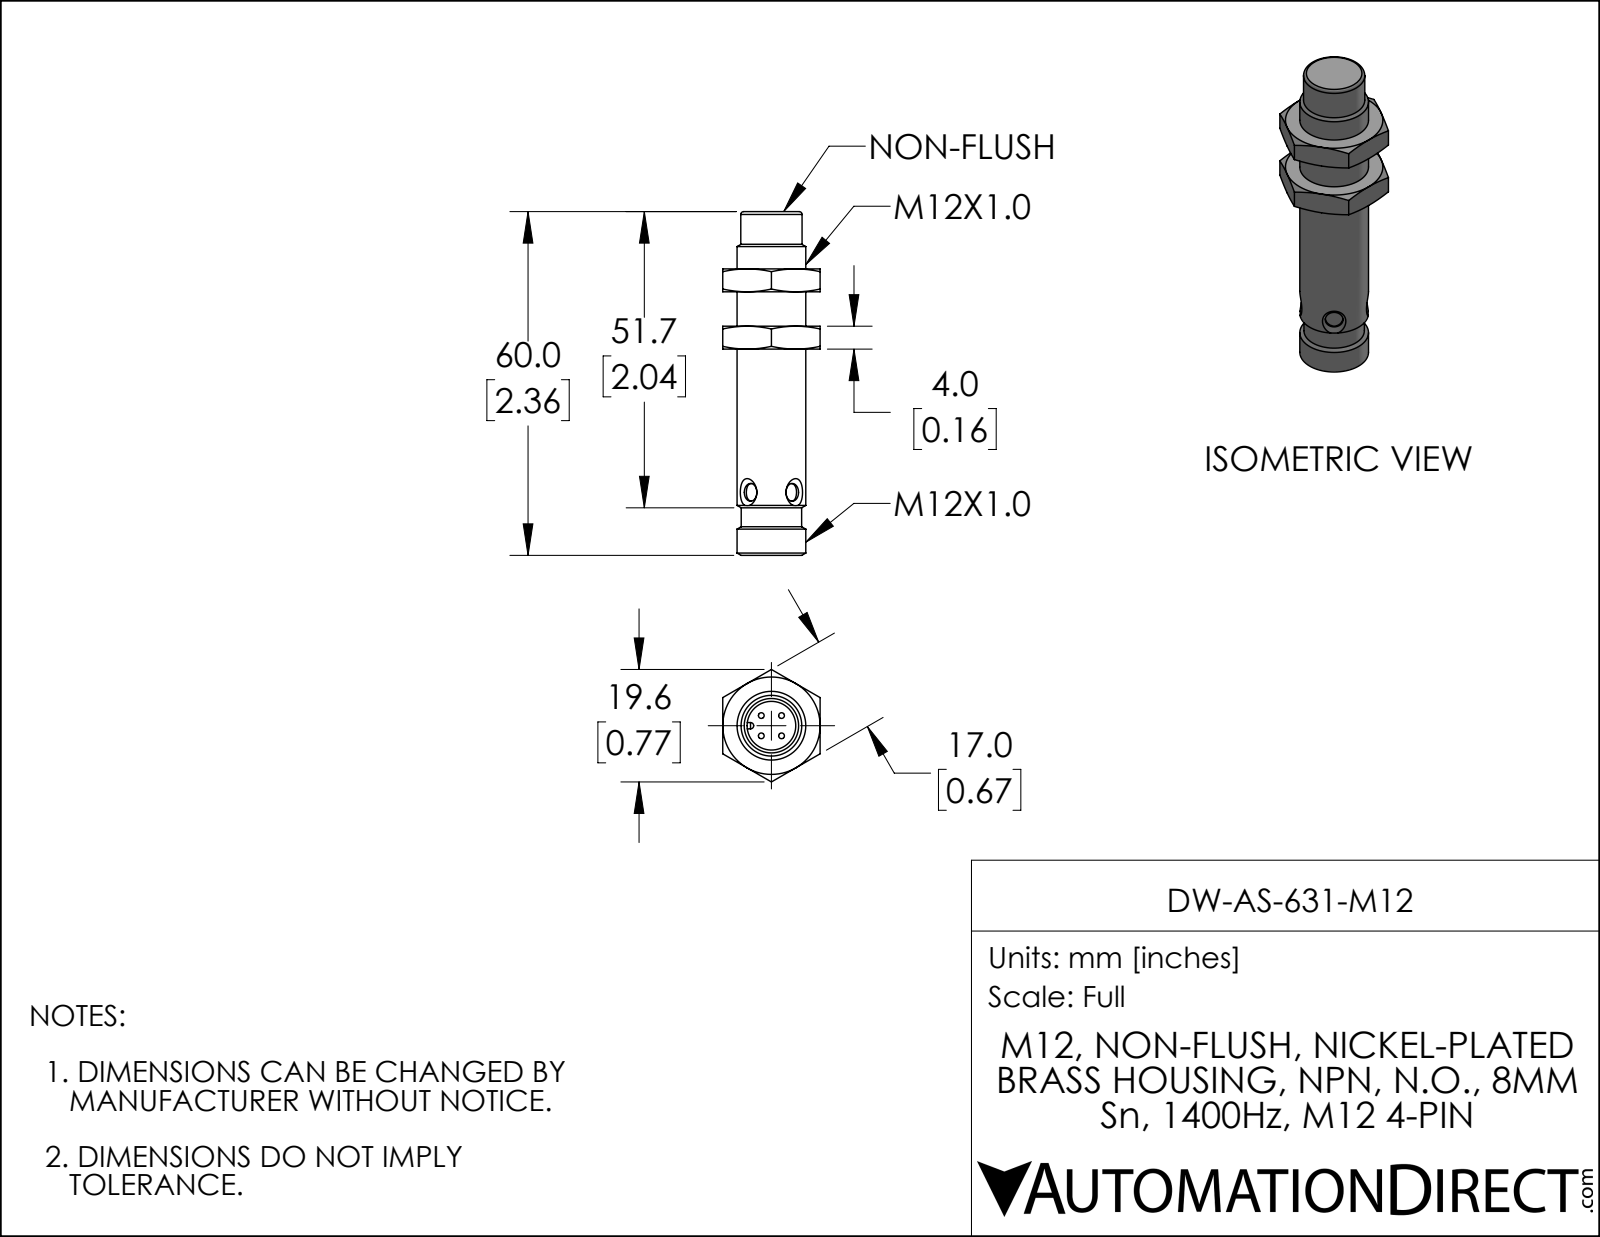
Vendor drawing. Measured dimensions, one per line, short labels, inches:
name: DW-AS-631-M12
written by: SolidWorks 2019 (AUTOMOTIVE_DESIGN)
unit: in
bodies: 1 solid, 82 faces (22 planar, 21 cylindrical, 39 other)
size: 2.362 × 0.773 × 0.669
volume: 0.435 in³; area: 5.403 in²
holes: 2× ⌀0.122, 1× ⌀0.335
bosses: 4× ⌀0.039, 1× ⌀0.472, 1× ⌀0.421, 1× ⌀0.415
rounds: 2× R0.022, 1× R0.193
face distances: 0.394, 0.157, 0.669, 0.551, 0.236, 0.787, 0.945, 2.022, 1.629, 1.471
